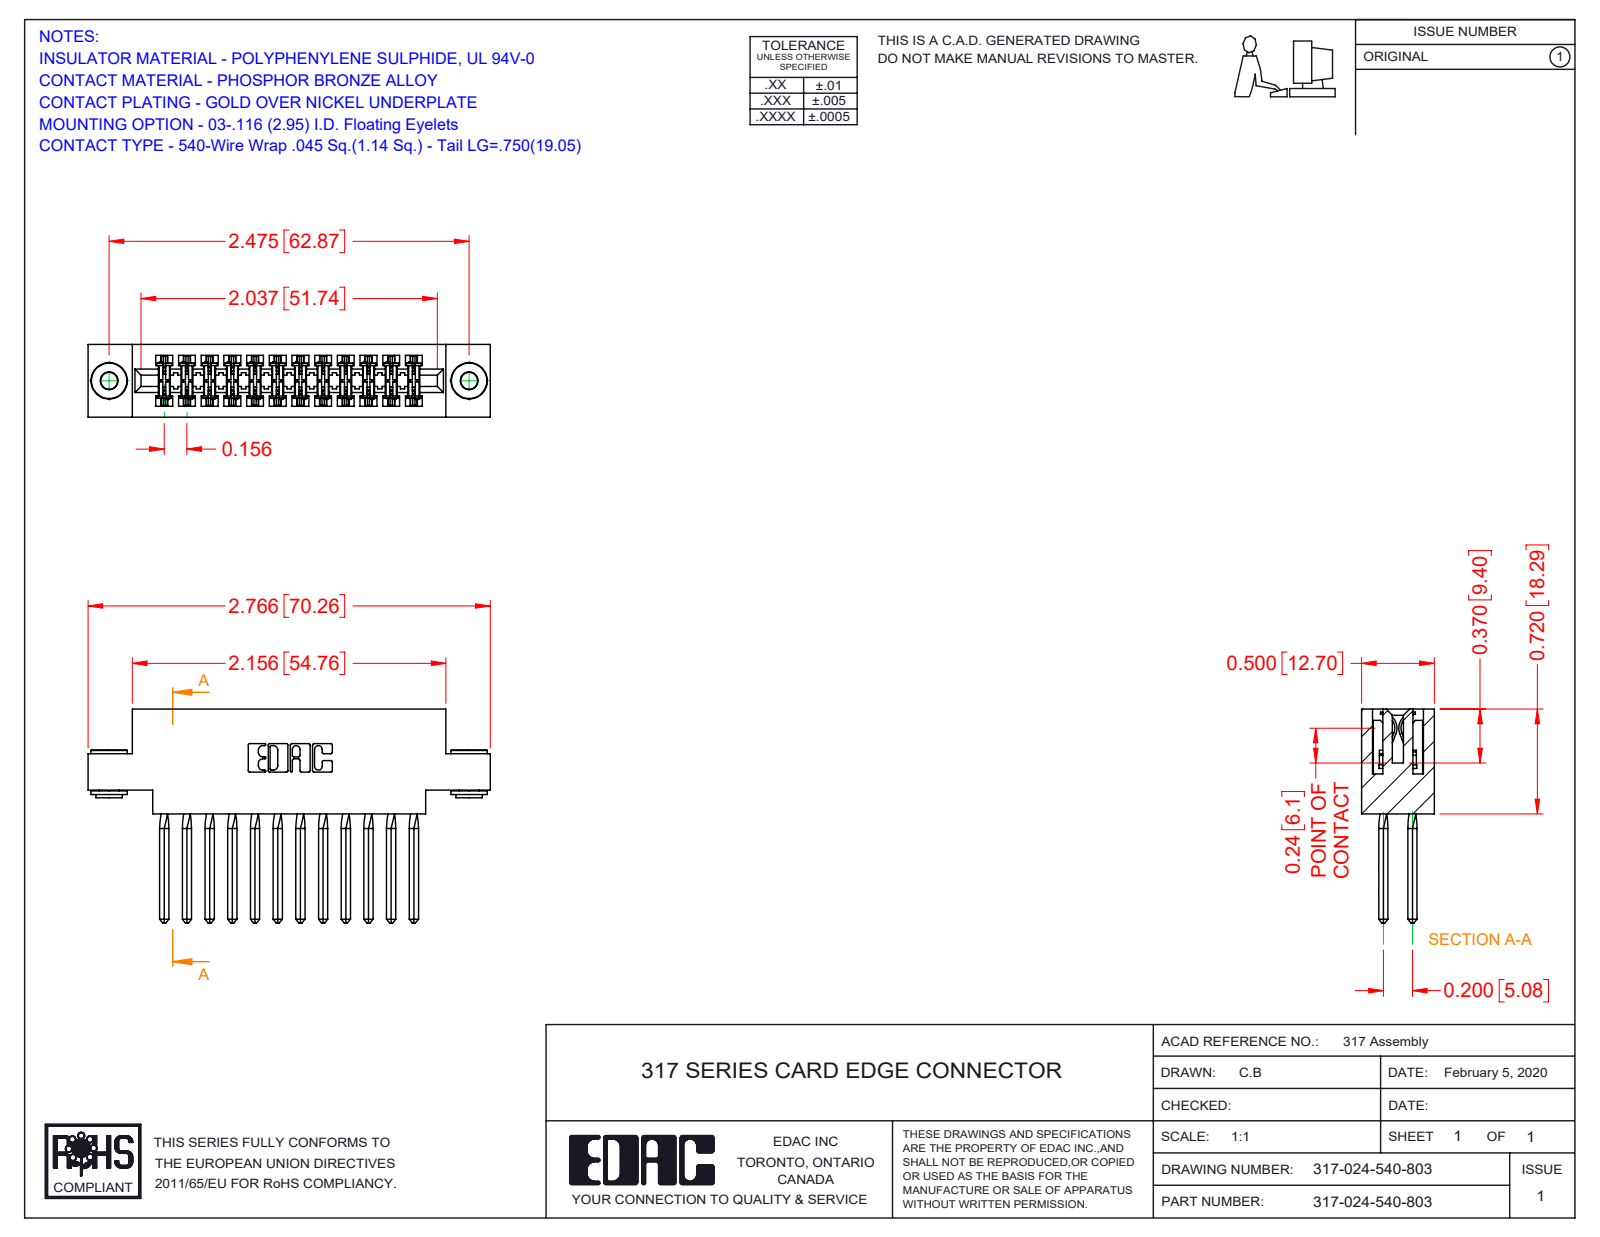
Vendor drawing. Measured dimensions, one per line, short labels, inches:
name: 345-250-002_345-250-002-102; 317-290-001_540; 317 Part_.156 Dia - TH; 317-024-540-803
written by: SolidWorks 2016 (CONFIG_CONTROL_DESIGN)
unit: in
bodies: 27 solids, 2276 faces (1820 planar, 352 cylindrical, 104 other)
size: 2.766 × 1.47 × 0.5
volume: 0.659 in³; area: 23.52 in²
holes: 2× ⌀0.116, 2× ⌀0.156
bosses: 2× ⌀0.25, 2× ⌀0.18, 2× ⌀0.136
rounds: 48× R0.015, 22× R0.01, 6× R0.007, 6× R0.031, 3× R0.026, 2× R0.095, 2× R0.1, 2× R0.11
face distances: 0.5, 0.075, 0.425, 0.11, 0.22, 0.35, 0.305, 0.331, 0.156, 0.72
hole spacings: 2.475
